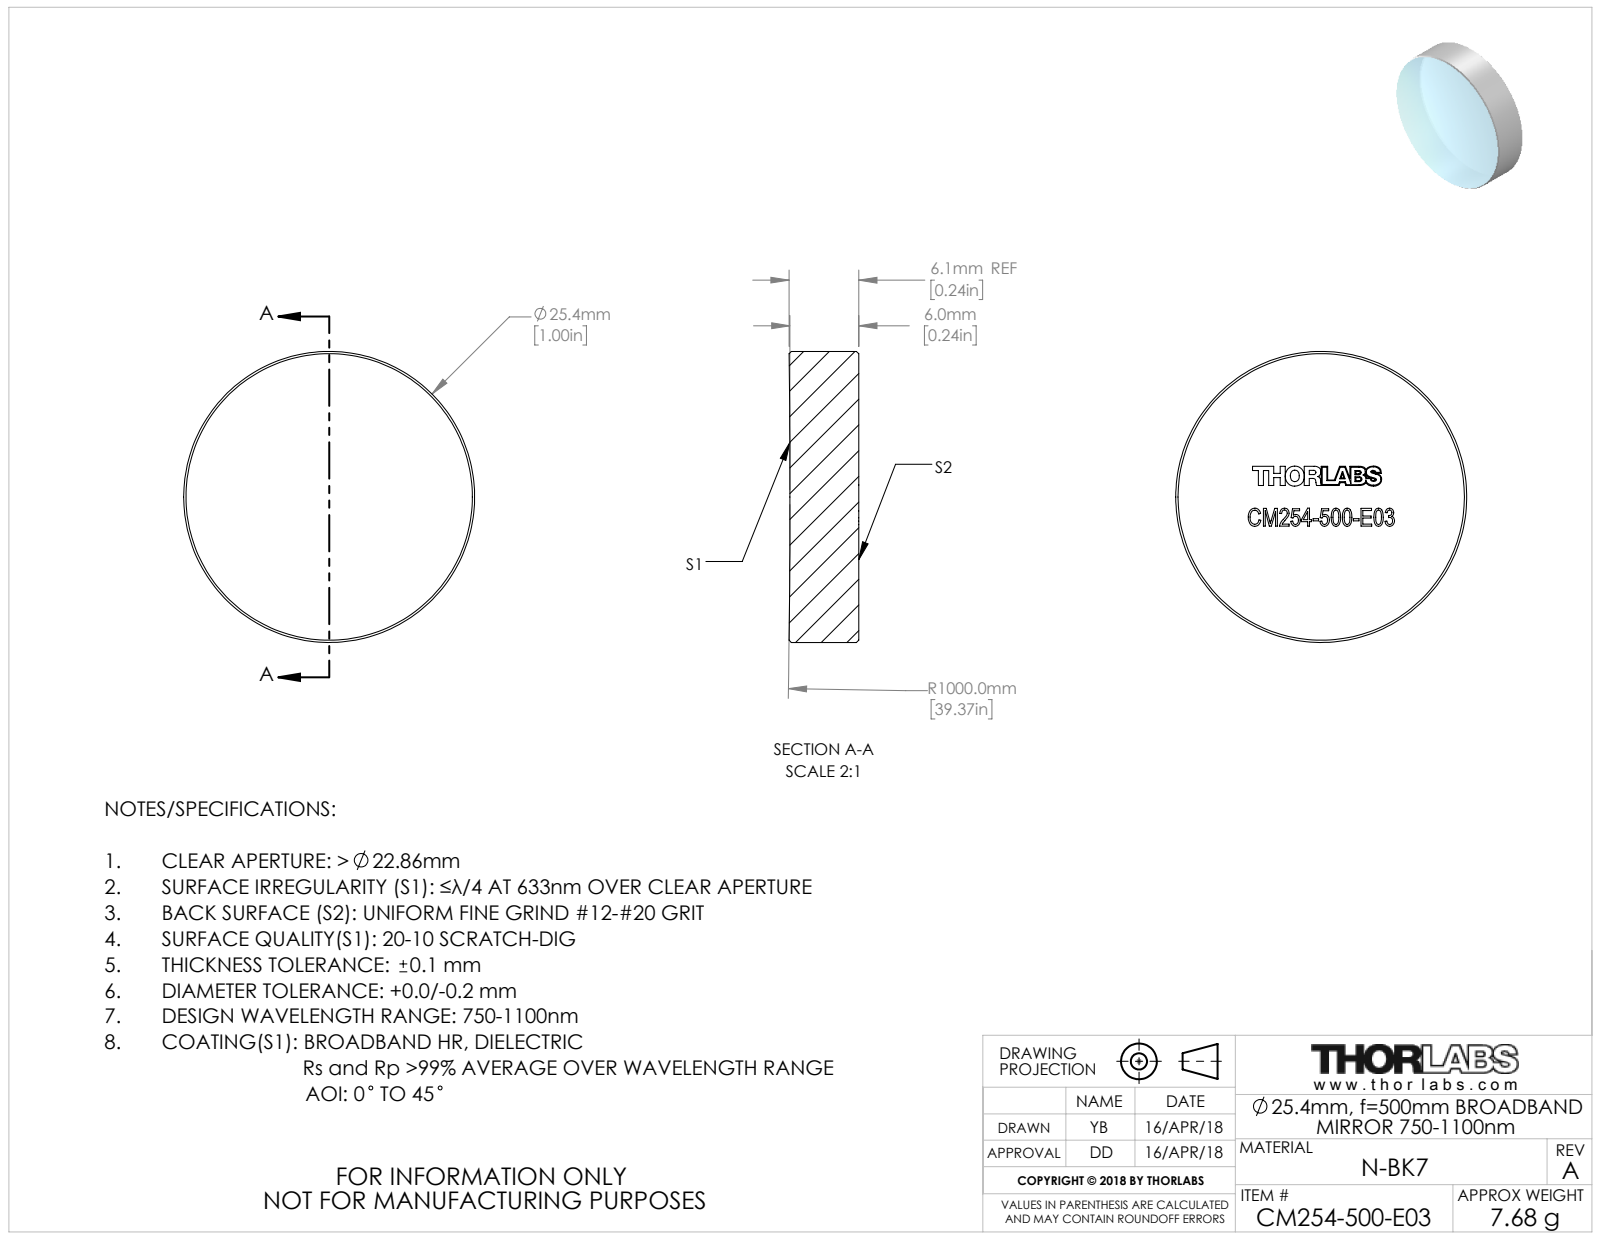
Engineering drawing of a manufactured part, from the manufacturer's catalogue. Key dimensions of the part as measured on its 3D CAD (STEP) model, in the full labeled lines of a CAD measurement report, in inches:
Part name (STEP PRODUCT): TTN153306-E0W
STEP written by: SolidWorks 2018 (CONFIG_CONTROL_DESIGN)
Units: inches
Bodies: 1 solid, 41 faces (33 planar, 2 cylindrical, 6 other)
Overall size (bounding box): 1 × 1 × 0.239
Volume: 0.187 in³ · Surface area: 2.294 in²
Round bosses / shafts (diameter × count): ⌀1 ×1
